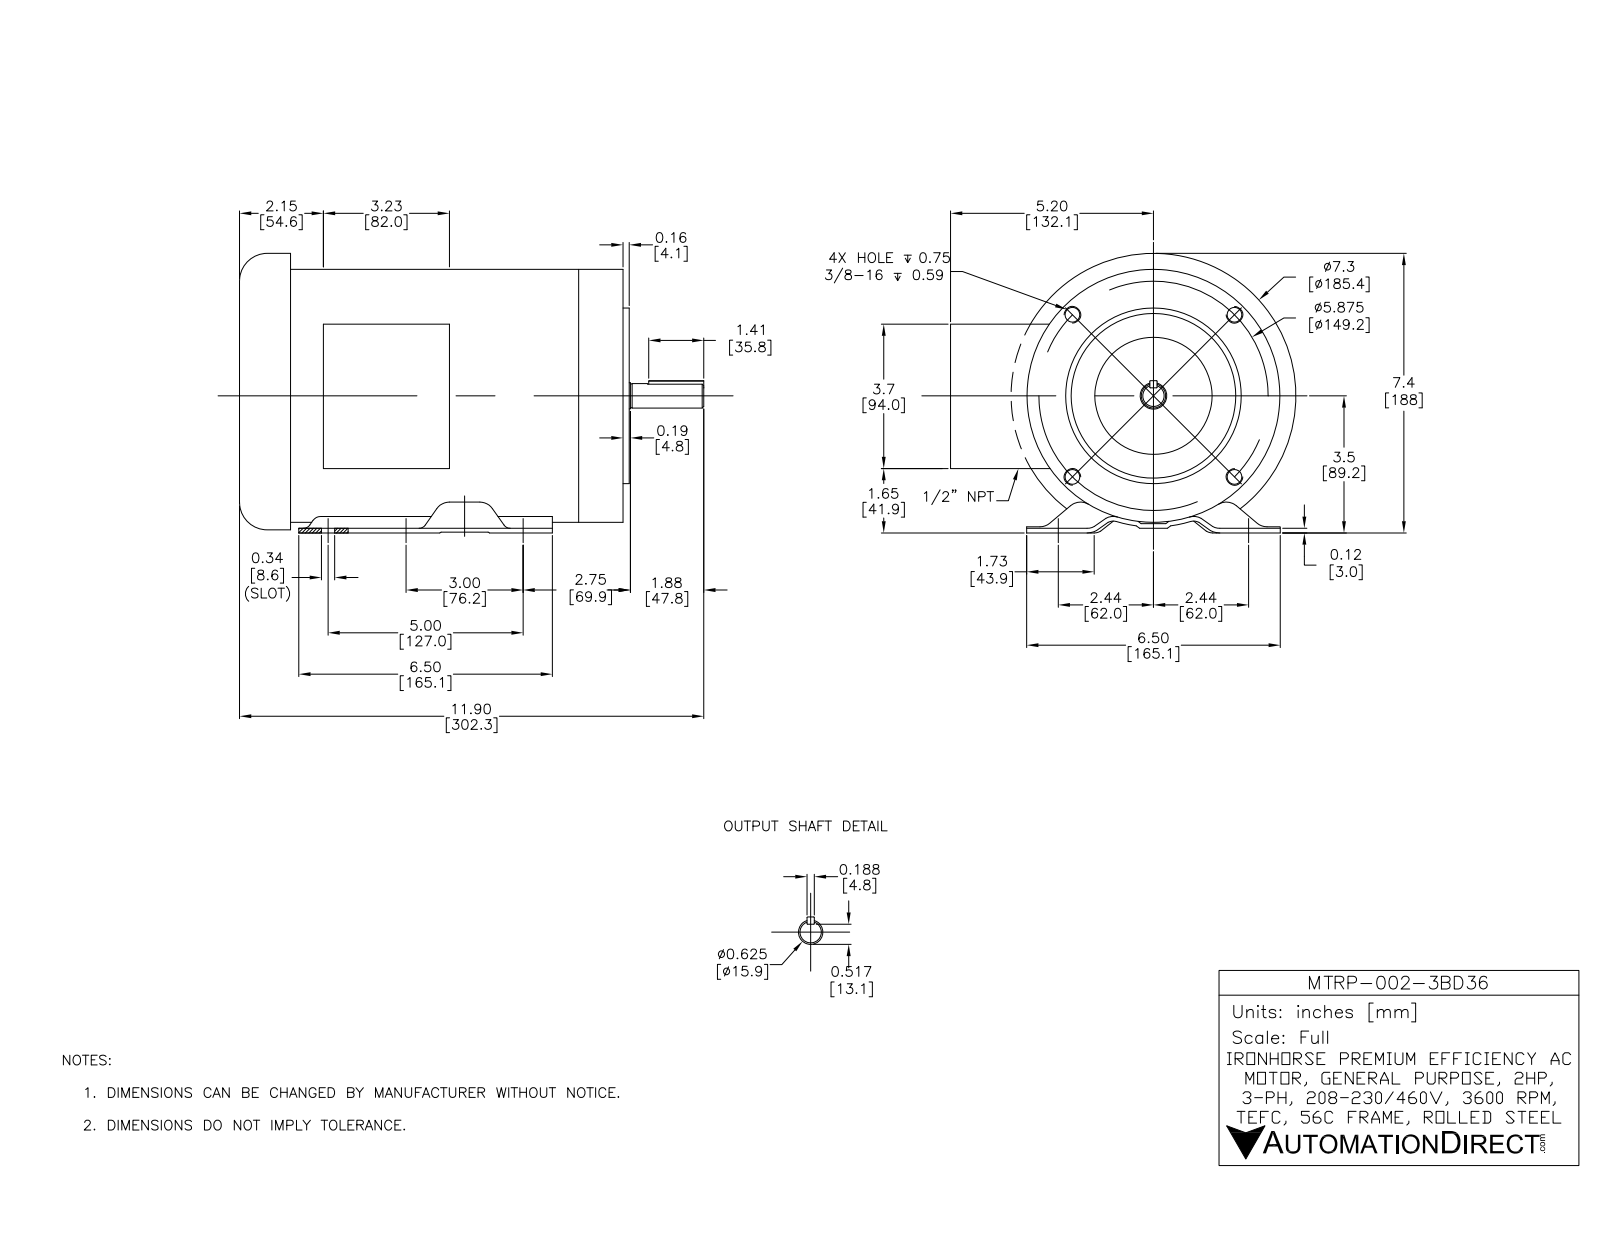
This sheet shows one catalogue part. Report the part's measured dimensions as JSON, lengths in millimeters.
{"part_name": "MTRP-002-BD36", "step_written_by": "SolidWorks 2016 (AUTOMOTIVE_DESIGN)", "units": "millimeters", "bodies": {"solids": 40, "faces": 3663, "planar": 821, "cylindrical": 1174, "other": 1668}, "overall_size": [299.1, 227.03, 183.73], "volume_mm3": 728366, "surface_area_mm2": 624276, "round_holes": [[5, 12], [5.56, 9], [7, 9], [5.5, 6], [6.93, 6], [8.73, 6], [3.45, 5], [3.8, 4], [4.5, 4], [7.94, 4], [1.7, 2], [3.4, 2]], "round_bosses_or_shafts": [[8.84, 9], [4.17, 9], [10.52, 6], [6.35, 6], [4.83, 6], [182.5, 1], [164, 1], [114.3, 1]], "partial_cylinders_radius": [[0.5, 204], [3, 123], [2, 43], [1, 38], [4, 32], [3.5, 26], [7, 19], [4.37, 12]], "face_to_face_distances": [3, 1, 1.6, 245, 244, 2, 90.4, 78.4, 1.2, 2.5], "hole_center_spacings": [107.22, 77, 2.39, 58.93, 61.2, 74.61, 75.67, 95.21]}
